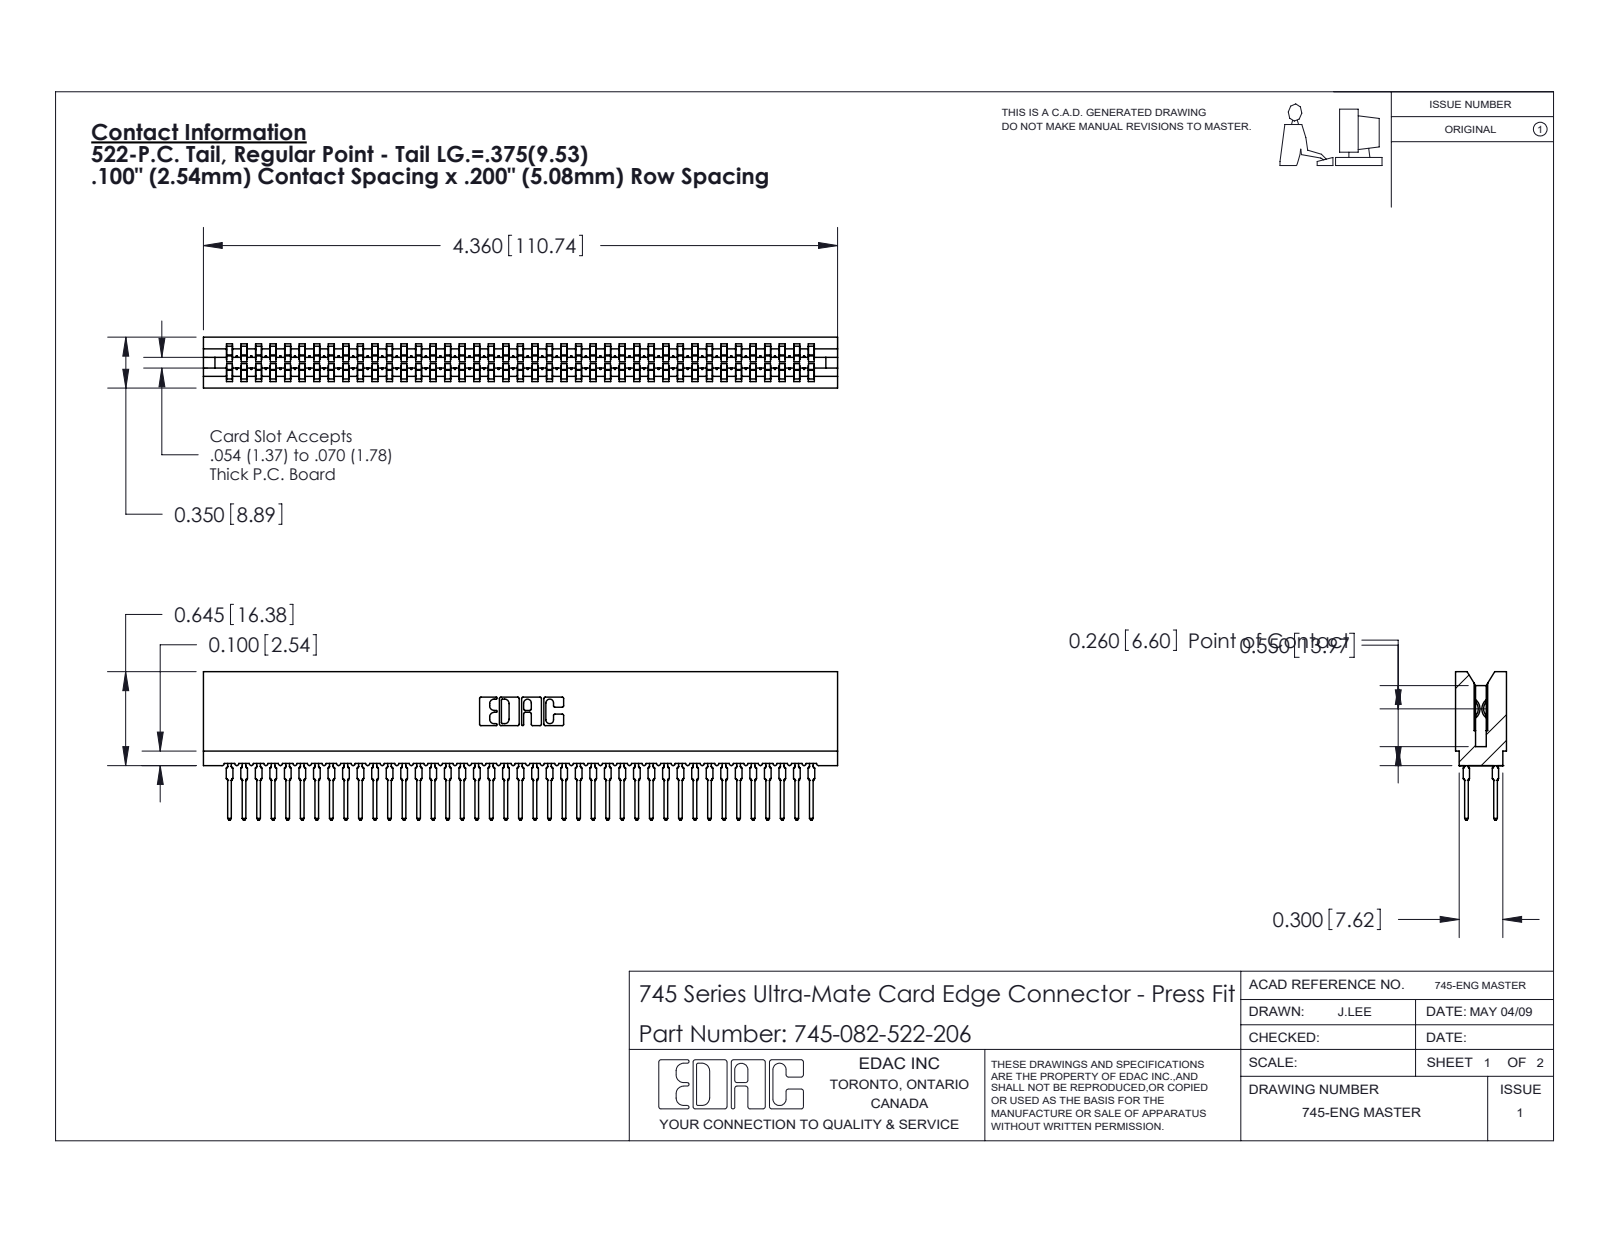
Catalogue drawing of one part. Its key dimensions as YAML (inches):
part_name: "745 Part_Insulator Option - 06; 745-292-001_522; 745-082-522-206"
step_written_by: "SolidWorks 2020 (CONFIG_CONTROL_DESIGN)"
units: inches
bodies: {solids: 83, faces: 7435, planar: 3828, cylindrical: 1475, other: 2132}
overall_size: [4.36, 1.021, 0.35]
volume: 0.613
surface_area: 32.09
partial_cylinders:
  - {radius: 0.021, count: 164}
  - {radius: 0.015, count: 82}
  - {radius: 0.01, count: 22}
  - {radius: 0.005, count: 8}
  - {radius: 0.011, count: 8}
  - {radius: 0.007, count: 6}
  - {radius: 0.031, count: 6}
  - {radius: 0.026, count: 3}
face_to_face_distances: [0.35, 0.063, 0.287, 0.2, 0.138, 0.212, 0.076, 0.149, 0.045, 0.305]
